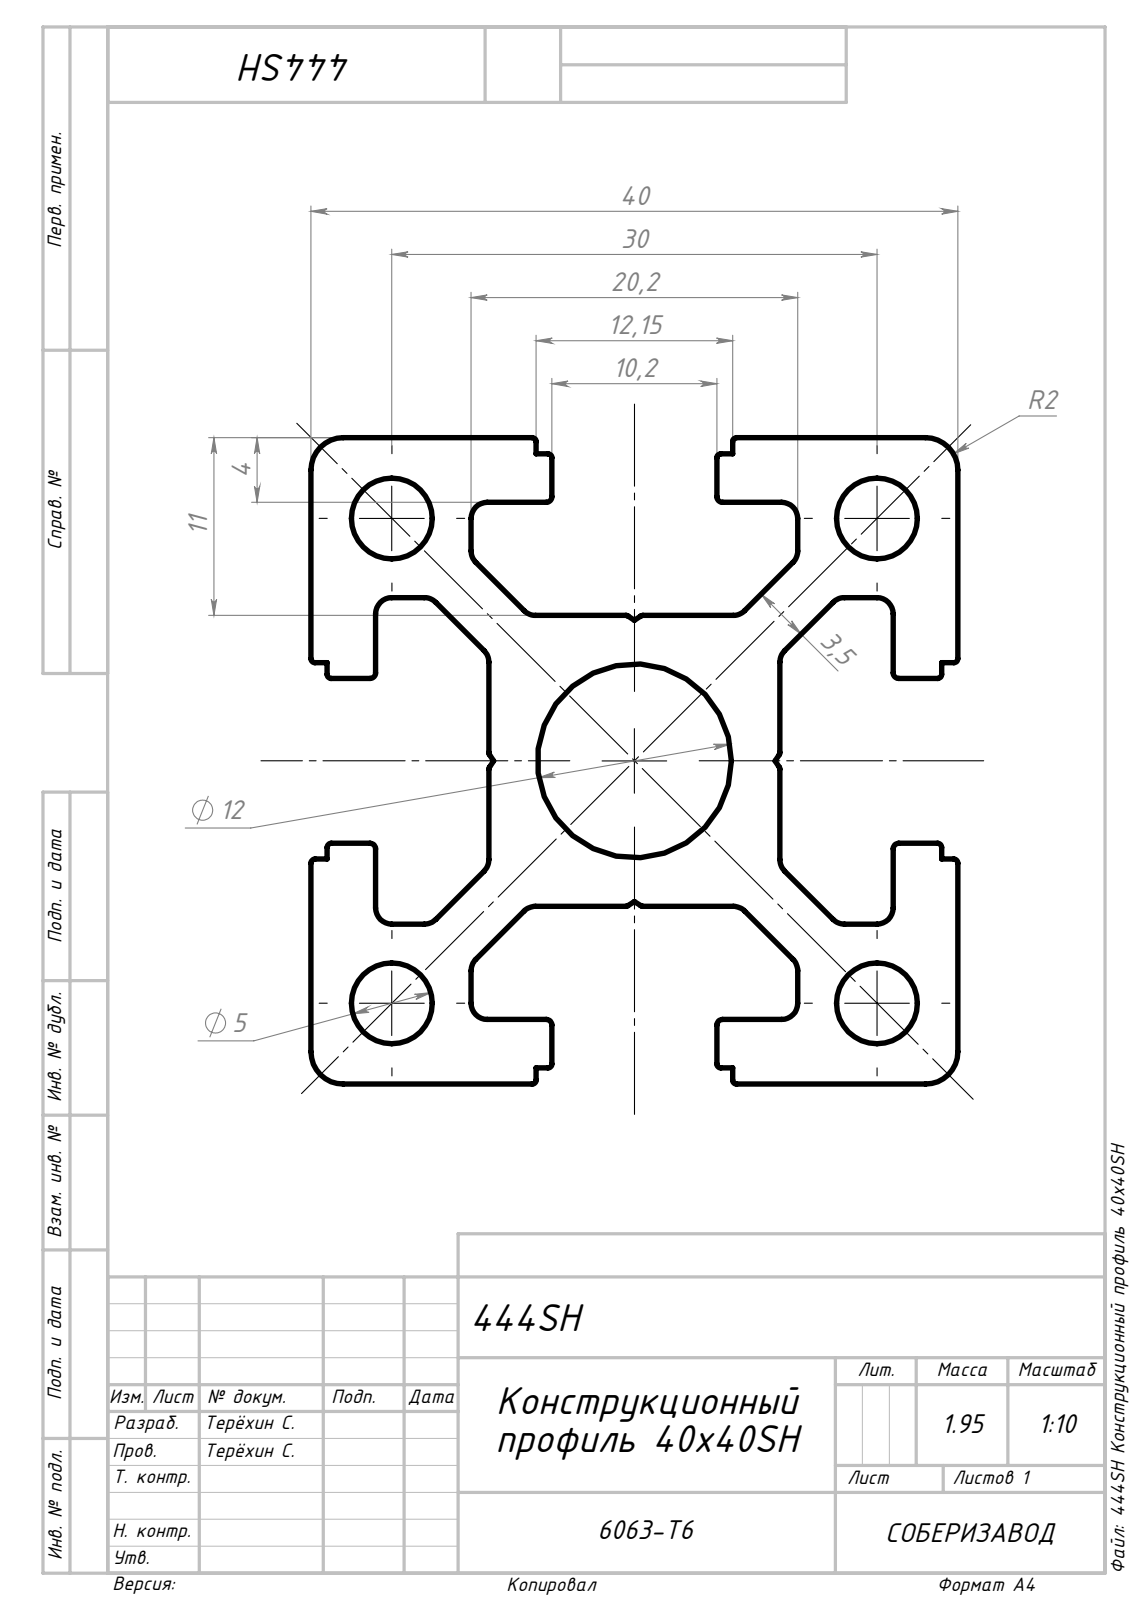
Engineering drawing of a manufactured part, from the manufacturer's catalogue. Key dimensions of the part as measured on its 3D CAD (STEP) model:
Part name (STEP PRODUCT): Сборка1
STEP written by: SolidWorks 2021 (AUTOMOTIVE_DESIGN)
Units: millimetres
Bodies: 1 solid, 152 faces (74 planar, 78 cylindrical, 0 other)
Overall size (bounding box): 1000 × 40 × 40
Volume: 720 540 mm³ · Surface area: 403 436 mm²
Round holes (diameter × count): ⌀5 ×4, ⌀12 ×1
Partial cylindrical surfaces — rounded edges, fillets, slot ends (radius × count): R0.25 ×24, R1 ×24, R0.35 ×8, R2 ×4
Main face-to-face distances: 40, 11, 29, 4, 36, 7, 25, 18, 14.9, 25.1
Hole centre spacings: 21.21, 30, 42.43
